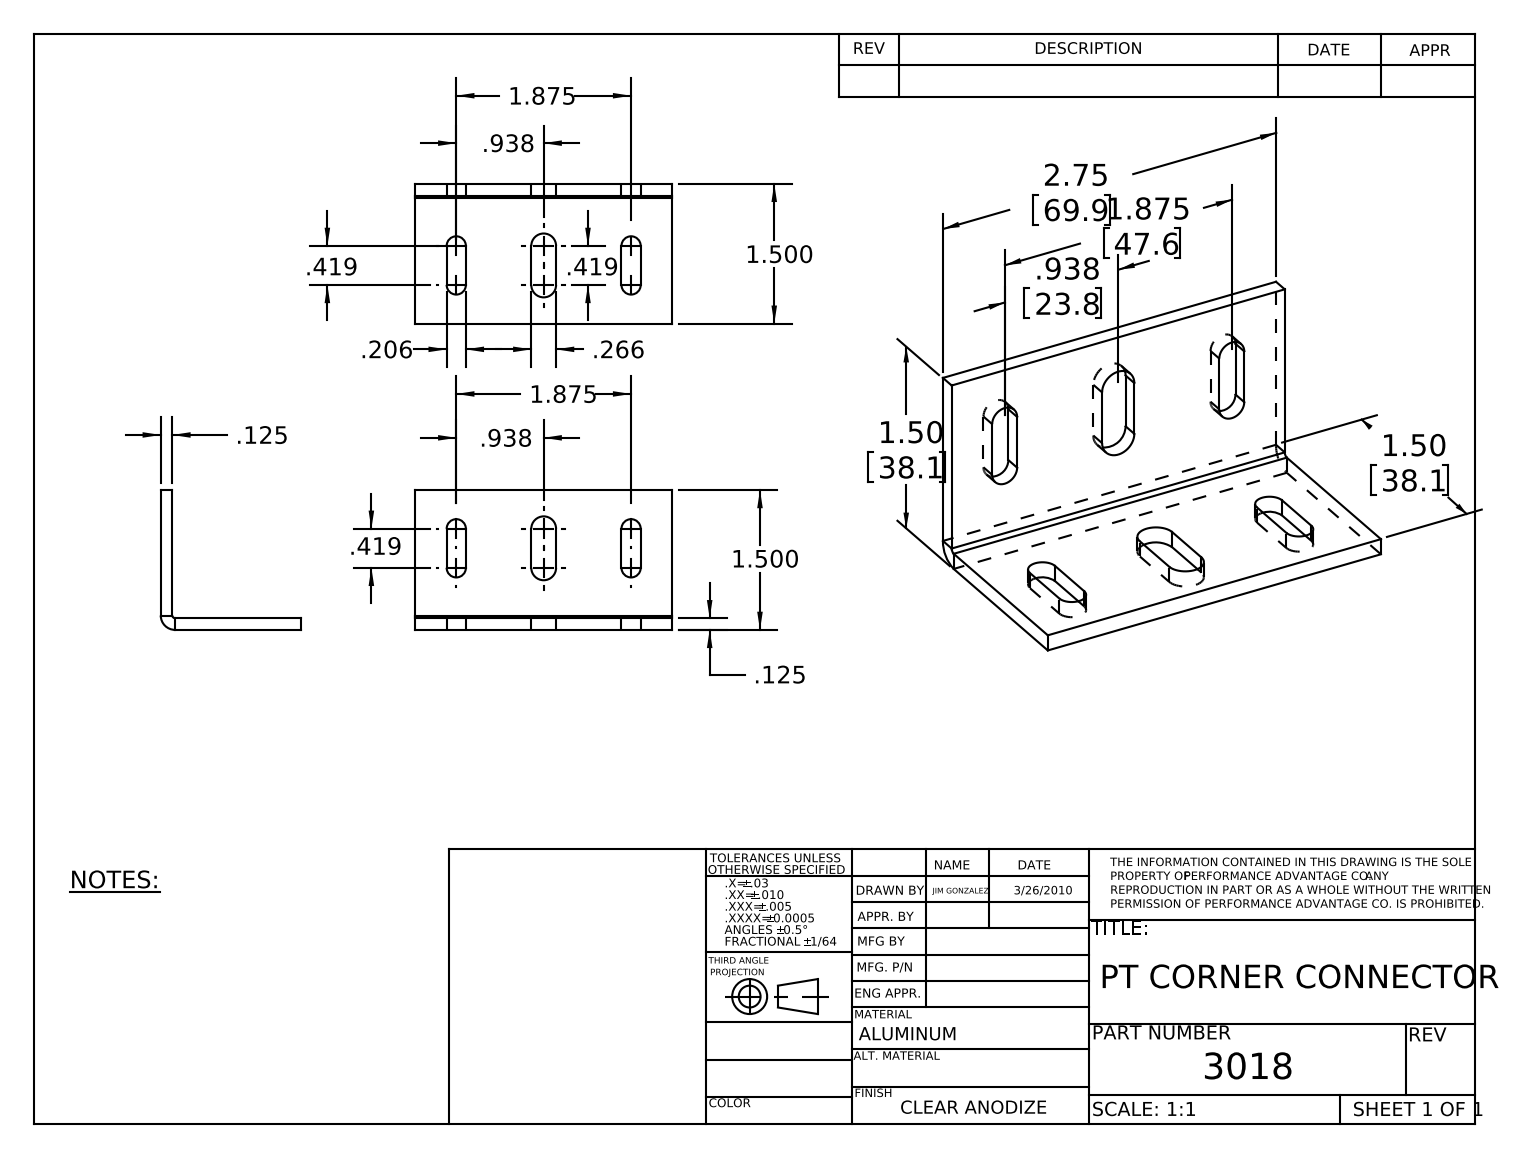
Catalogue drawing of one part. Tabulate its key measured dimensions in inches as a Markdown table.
| quantity | value |
| --- | --- |
| part name | 3018 |
| STEP written by | SolidWorks 2010 (CONFIG_CONTROL_DESIGN) |
| units | inches |
| bodies | 1 solid, 41 faces (24 planar, 17 cylindrical, 0 other) |
| overall size | 2.75 × 1.5 × 1.5 |
| volume | 0.873 in³ |
| surface area | 16.53 in² |
| partial cylindrical surfaces (radius × count) | 0.103 × 8, 0.133 × 4, 0.029 × 1, 0.154 × 1 |
| main face-to-face distances | 0.125, 1.375, 1.5, 2.75, 0.334, 0.54, 1.242, 1.508, 2.209, 2.415 |
